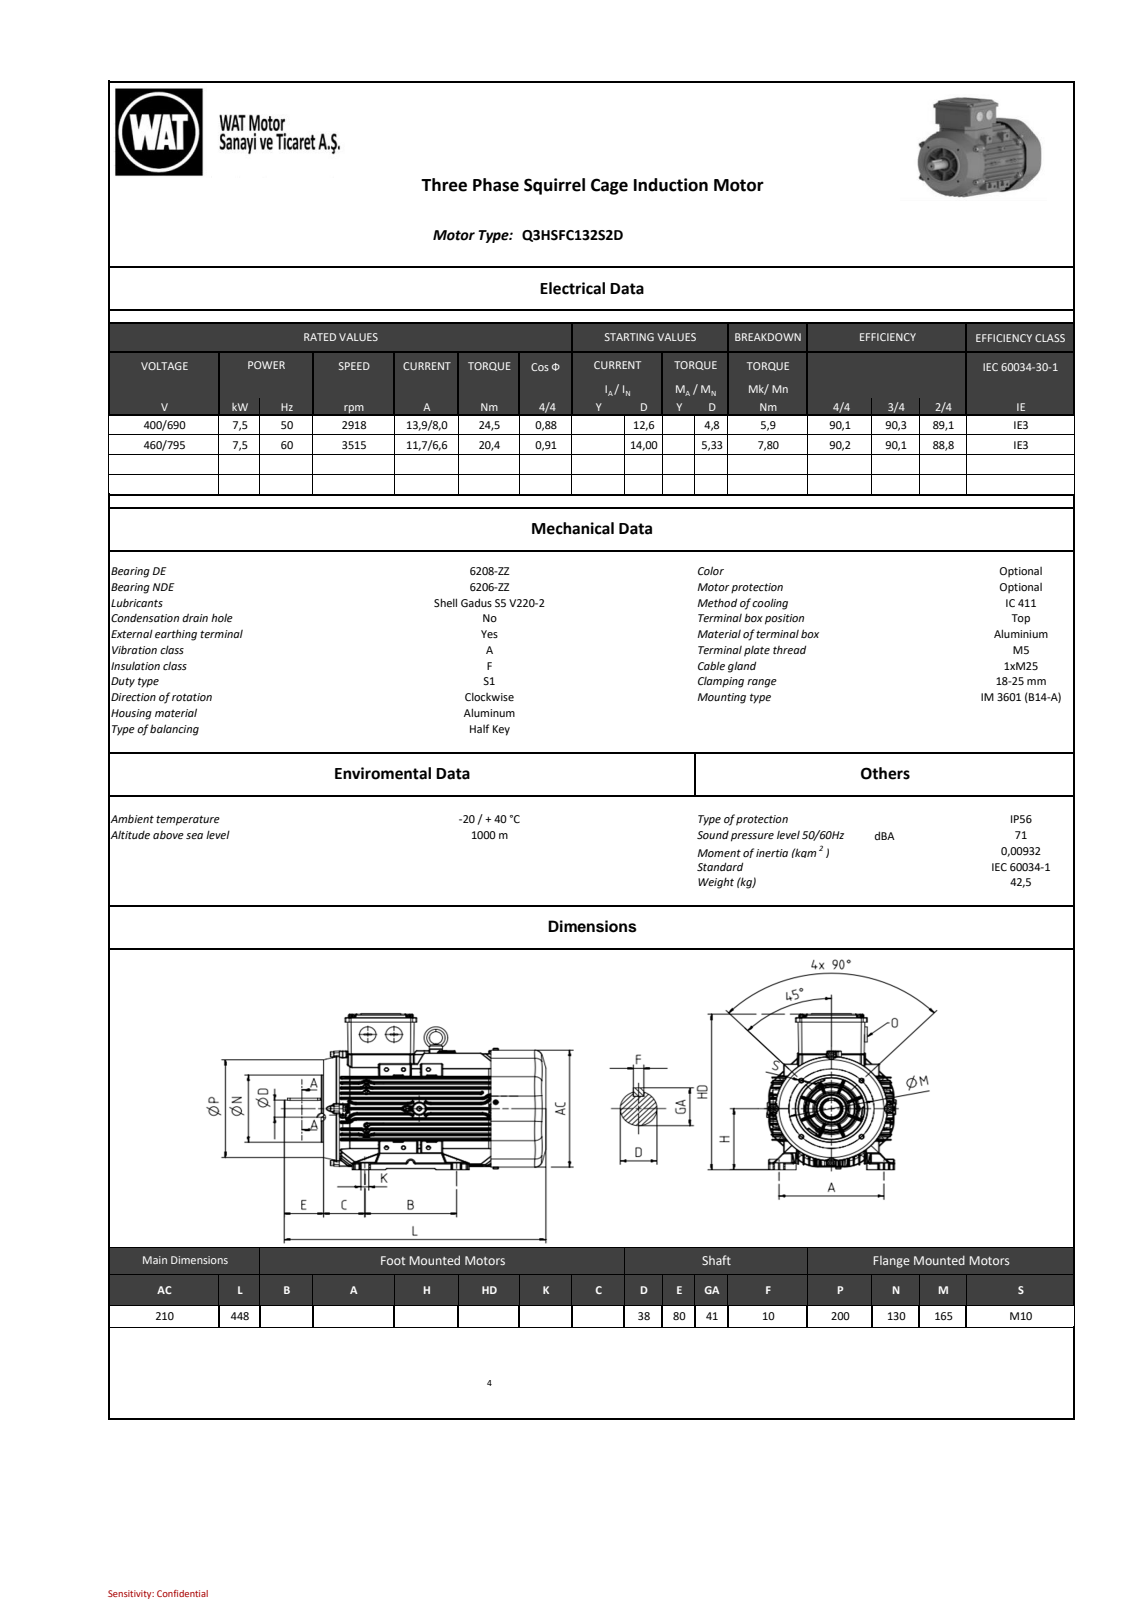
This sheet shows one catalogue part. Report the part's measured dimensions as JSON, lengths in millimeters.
{"part_name": "QHS series_ 132_B14a _DEEP COVER__stp_objects", "step_written_by": "SIEMENS PLM Software NX2206.8101 (AP203_CONFIGURATION_CONTROLLED_3D_DESIGN_OF_MECHANICAL_PARTS_AND_ASSEMBLIES_MIM_LF)", "units": "millimeters", "bodies": {"solids": 0, "faces": 6767, "planar": 1523, "cylindrical": 2580, "other": 2664}, "overall_size": [447.4, 257.59, 219], "round_holes": [[8.5, 4], [12, 2], [23.38, 2], [3.5, 1], [4, 1], [8, 1], [13, 1], [47, 1], [57.4, 1], [58.67, 1], [68, 1]], "round_bosses_or_shafts": [[8, 7], [10, 2], [6, 2], [188, 1], [130, 1], [61, 1], [40, 1], [38, 1]], "partial_cylinders_radius": [[2, 627], [0.8, 519], [1, 420], [0.5, 307], [3, 63], [4, 8], [5, 6], [3.5, 4]], "face_to_face_distances": [1, 10.99, 21.5, 35.96, 99.54, 90.43, 24.97, 68.93, 8.16, 112.88], "hole_center_spacings": [82.51, 116.68, 40, 165.01, 82.39, 82.62]}
